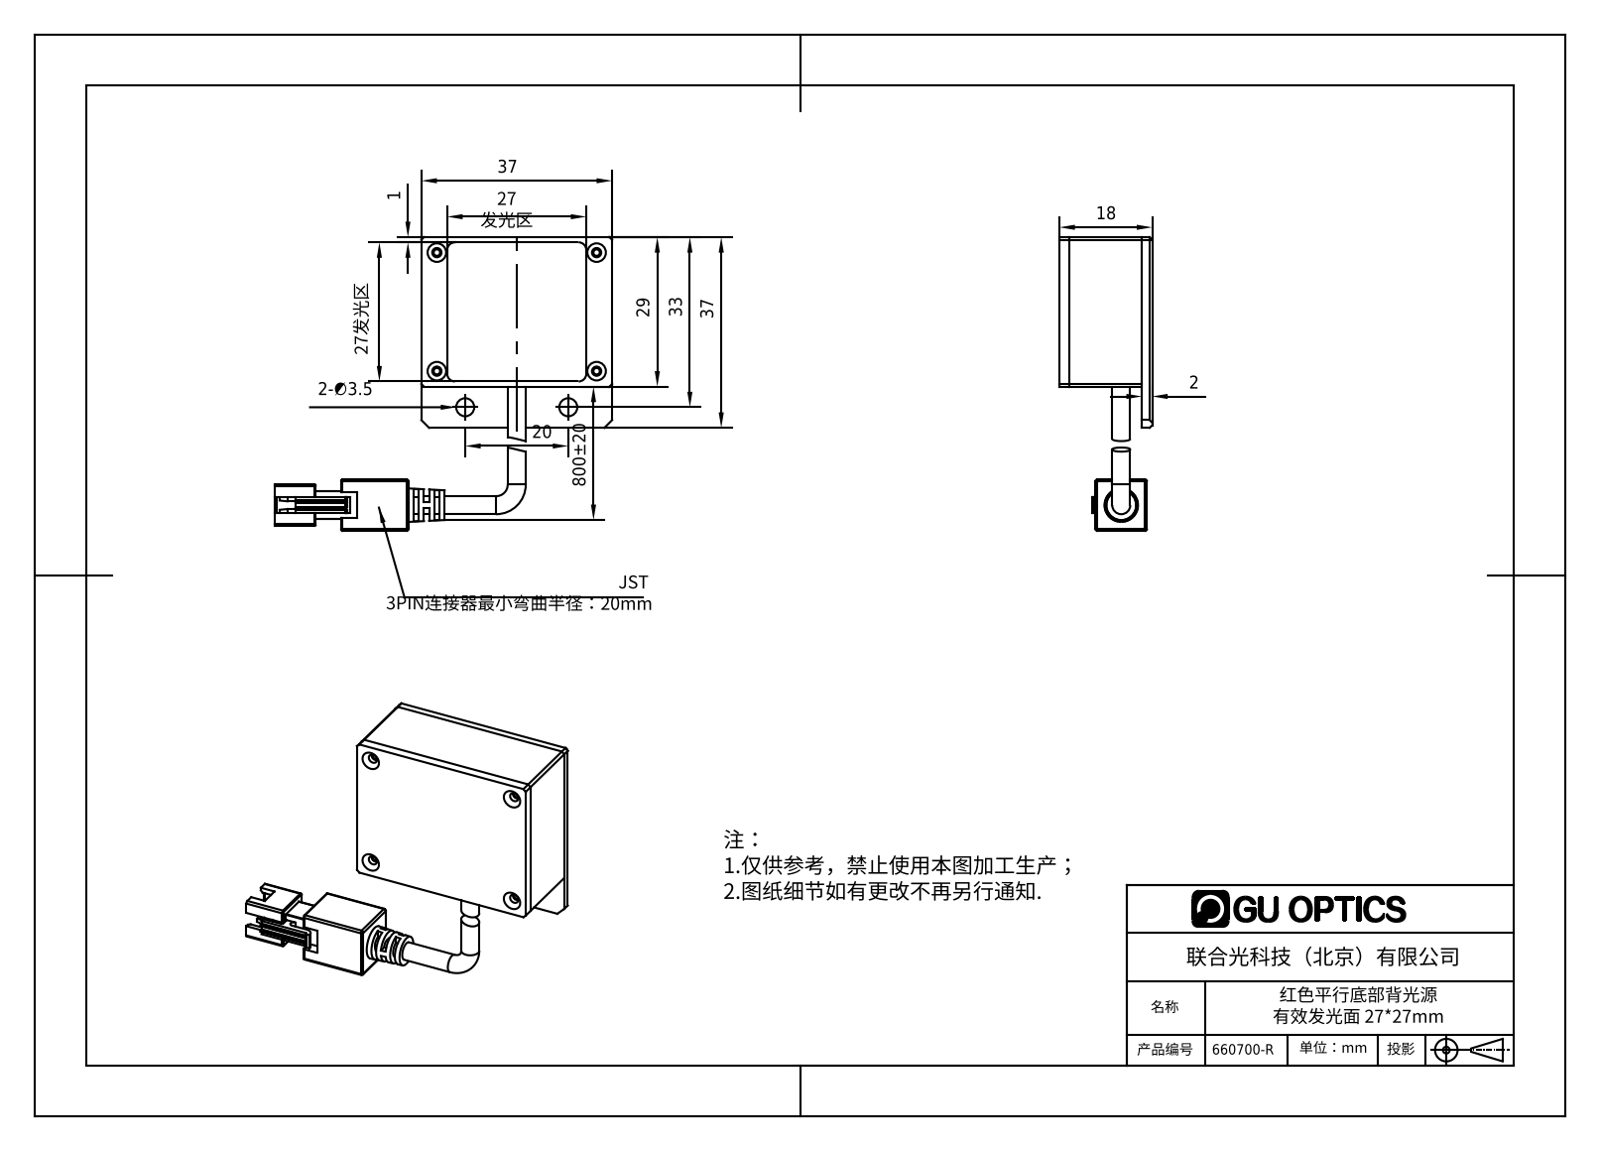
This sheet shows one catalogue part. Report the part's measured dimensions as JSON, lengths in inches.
{"part_name": "P-F3729-X-V1.0盖板; 两芯光源线(母端); P-F3729-X-V1.0漫射板; PFP-2727-H18X-A1.0 (+1 more)", "step_written_by": "SolidWorks 2014 (CONFIG_CONTROL_DESIGN)", "units": "inches", "bodies": {"solids": 5, "faces": 350, "planar": 169, "cylindrical": 119, "other": 62}, "overall_size": [2.579, 2.244, 0.709], "volume_in3": 0.705, "surface_area_in2": 18.01, "round_holes": [[0.049, 4], [0.063, 4], [0.071, 4], [0.079, 4], [0.094, 4], [0.138, 2]], "round_bosses_or_shafts": [[0.138, 2]], "partial_cylinders_radius": [[0.004, 15], [0.008, 13], [0.016, 12], [0.039, 4], [0.059, 4], [0.012, 1], [0.027, 1], [0.055, 1]], "face_to_face_distances": [0.079, 0.63, 0.551, 0.039, 0.709, 1.102, 0.197, 1.142, 1.063, 1.26], "hole_center_spacings": [0.35, 0.906, 1.041, 1.201, 1.22, 1.52, 1.55, 0.787]}
